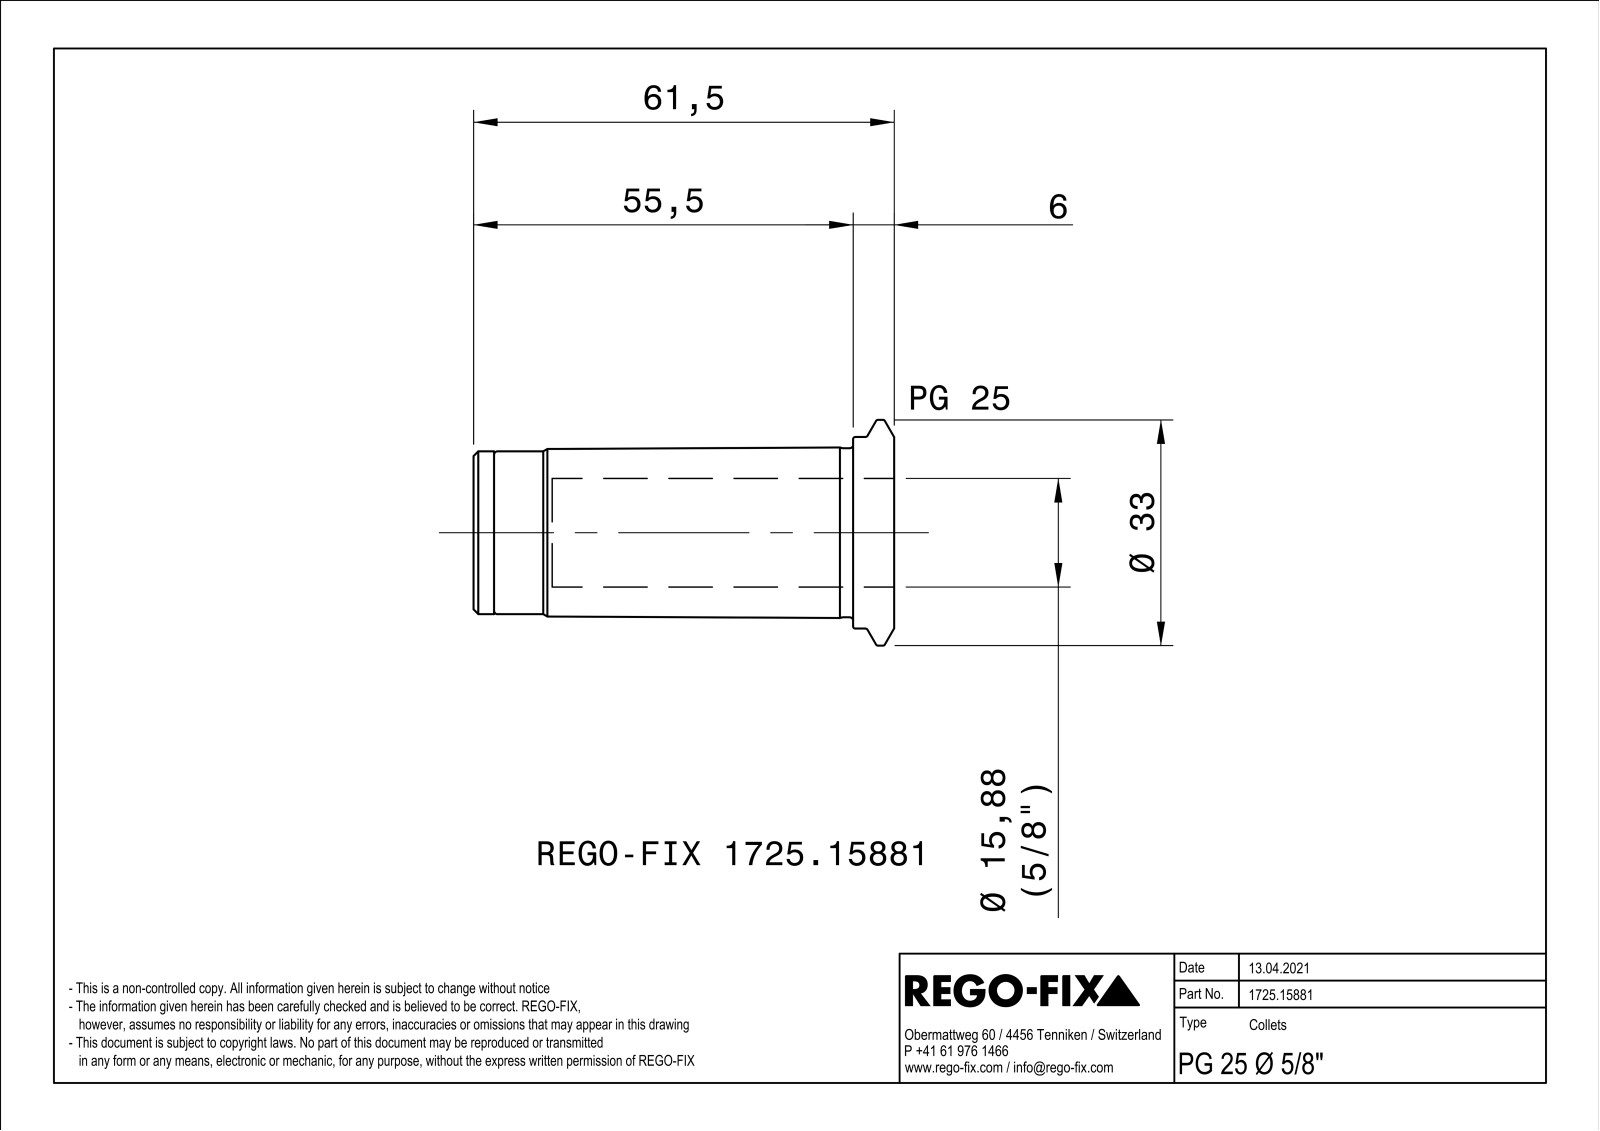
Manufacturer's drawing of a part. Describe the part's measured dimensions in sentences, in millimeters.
The part is named "NOCUT". Its 3-D file was written by "SIEMENS PLM Software Solid Edge ST10 (AUTOMOTIVE_DESIGN)". It is 1 solid with 85 faces: 23 planar, 23 cylindrical and 39 other. Overall it measures 60.5 by 33 by 32.99 millimeters. Round holes: 3 of diameter 2.5, 1 of diameter 5.2, 1 of diameter 6.92, 1 of diameter 8.2, 1 of diameter 15.88, 1 of diameter 20.4, 1 of diameter 20.92, 1 of diameter 22.2. Round bosses or shafts: 1 of diameter 33, 1 of diameter 28, 1 of diameter 24.7, 1 of diameter 23.8, 1 of diameter 12. The main face-to-face distances are 1, 60.5, 52.6, 7.9, 58.5, 5.9, 2, 50, 2.6, 8.5. The hole center spacings are 7.75, 13.43, 13.42.
